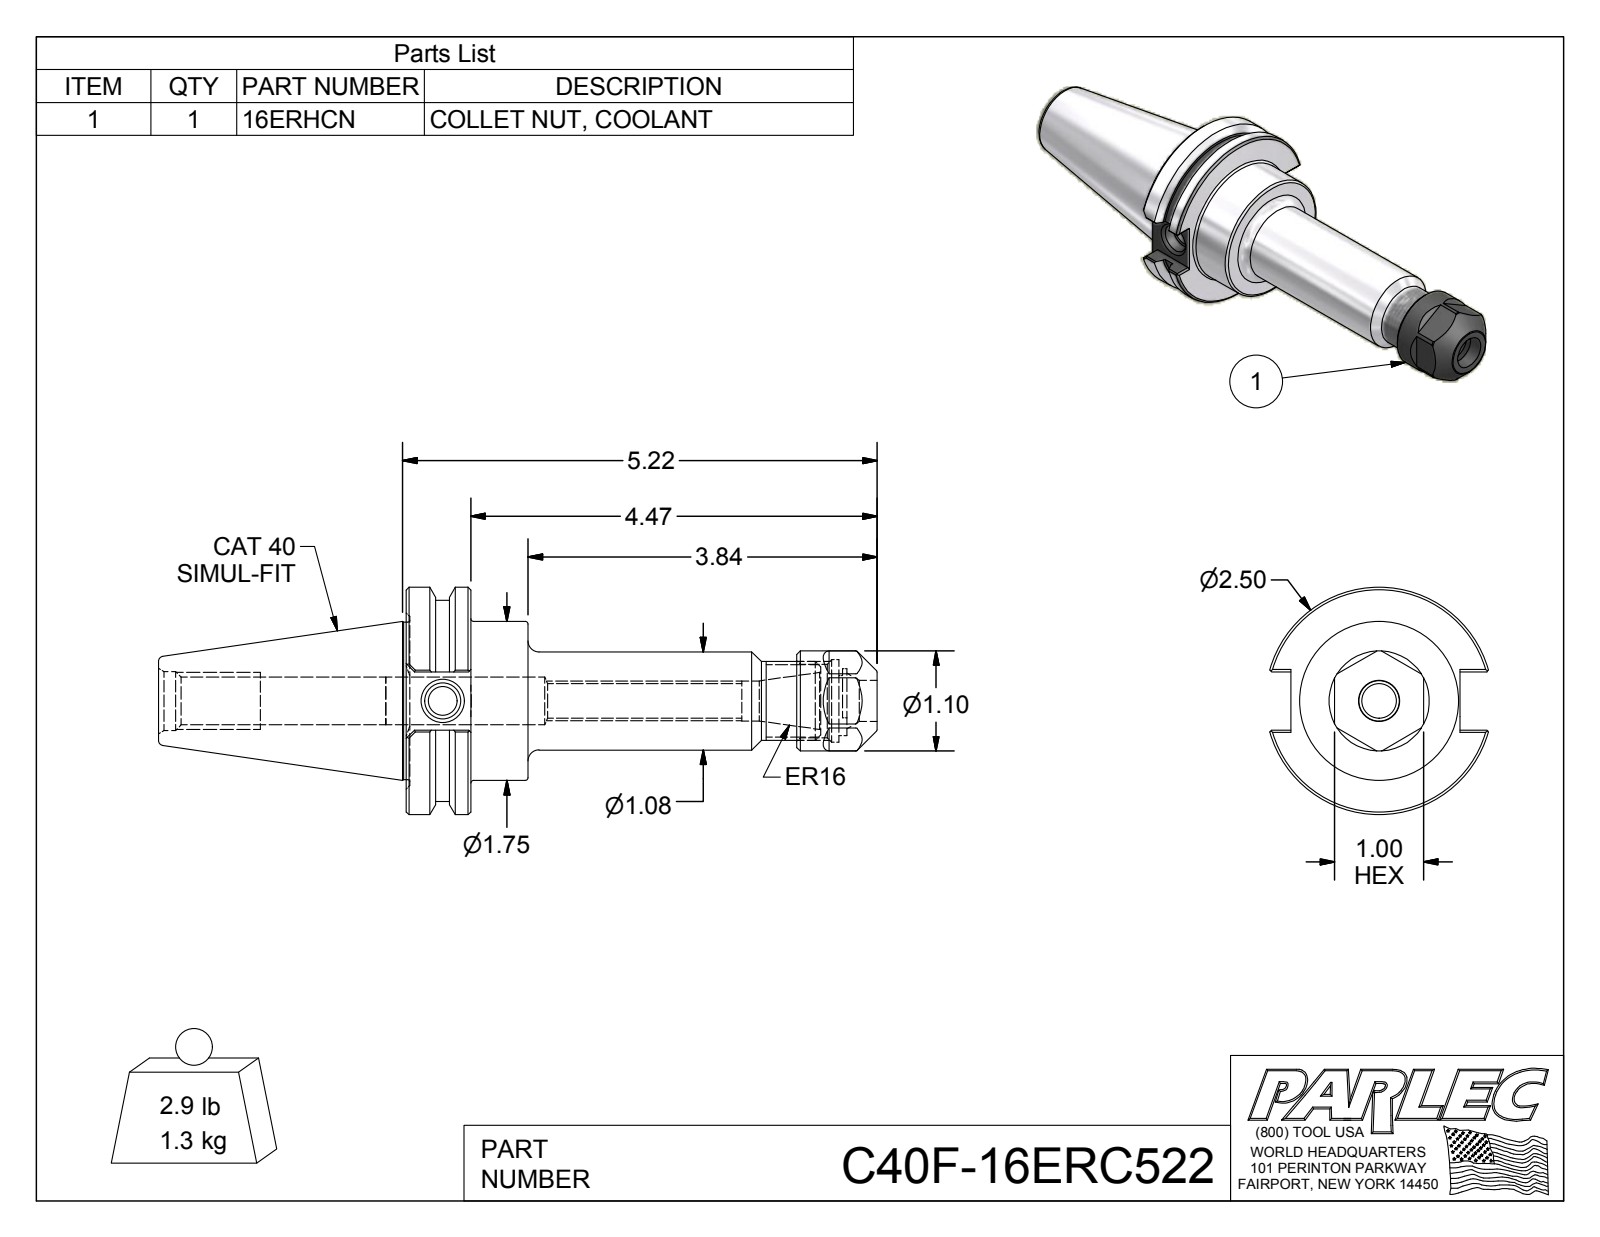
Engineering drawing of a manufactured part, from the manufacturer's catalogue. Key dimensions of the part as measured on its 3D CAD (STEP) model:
Part name (STEP PRODUCT): C40F-16ERC522; C40F-16ER5-1; 16ERHCN
STEP written by: Autodesk Inventor 2012 (AUTOMOTIVE_DESIGN)
Units: inches
Bodies: 2 solids, 116 faces (51 planar, 23 cylindrical, 42 other)
Overall size (bounding box): 7.908 × 2.5 × 2.406
Volume: 10.28 in³ · Surface area: 56.62 in²
Round holes (diameter × count): ⌀0.315 ×1, ⌀0.383 ×1, ⌀0.399 ×1, ⌀0.44 ×1, ⌀0.453 ×1, ⌀0.527 ×1, ⌀0.527 ×1, ⌀0.648 ×1, ⌀0.661 ×1, ⌀0.807 ×1, ⌀0.906 ×1
Round bosses / shafts (diameter × count): ⌀2.5 ×1, ⌀2.215 ×1, ⌀1.75 ×1, ⌀1.73 ×1, ⌀1.102 ×1, ⌀1.08 ×1, ⌀0.866 ×1
Partial cylindrical surfaces — rounded edges, fillets, slot ends (radius × count): R0.354 ×1
Main face-to-face distances: 0.71, 1.34, 0.63, 0.979, 4.759, 4.049, 3.419, 1.86, 0.64, 0.037
Hole centre spacings: 0.051
